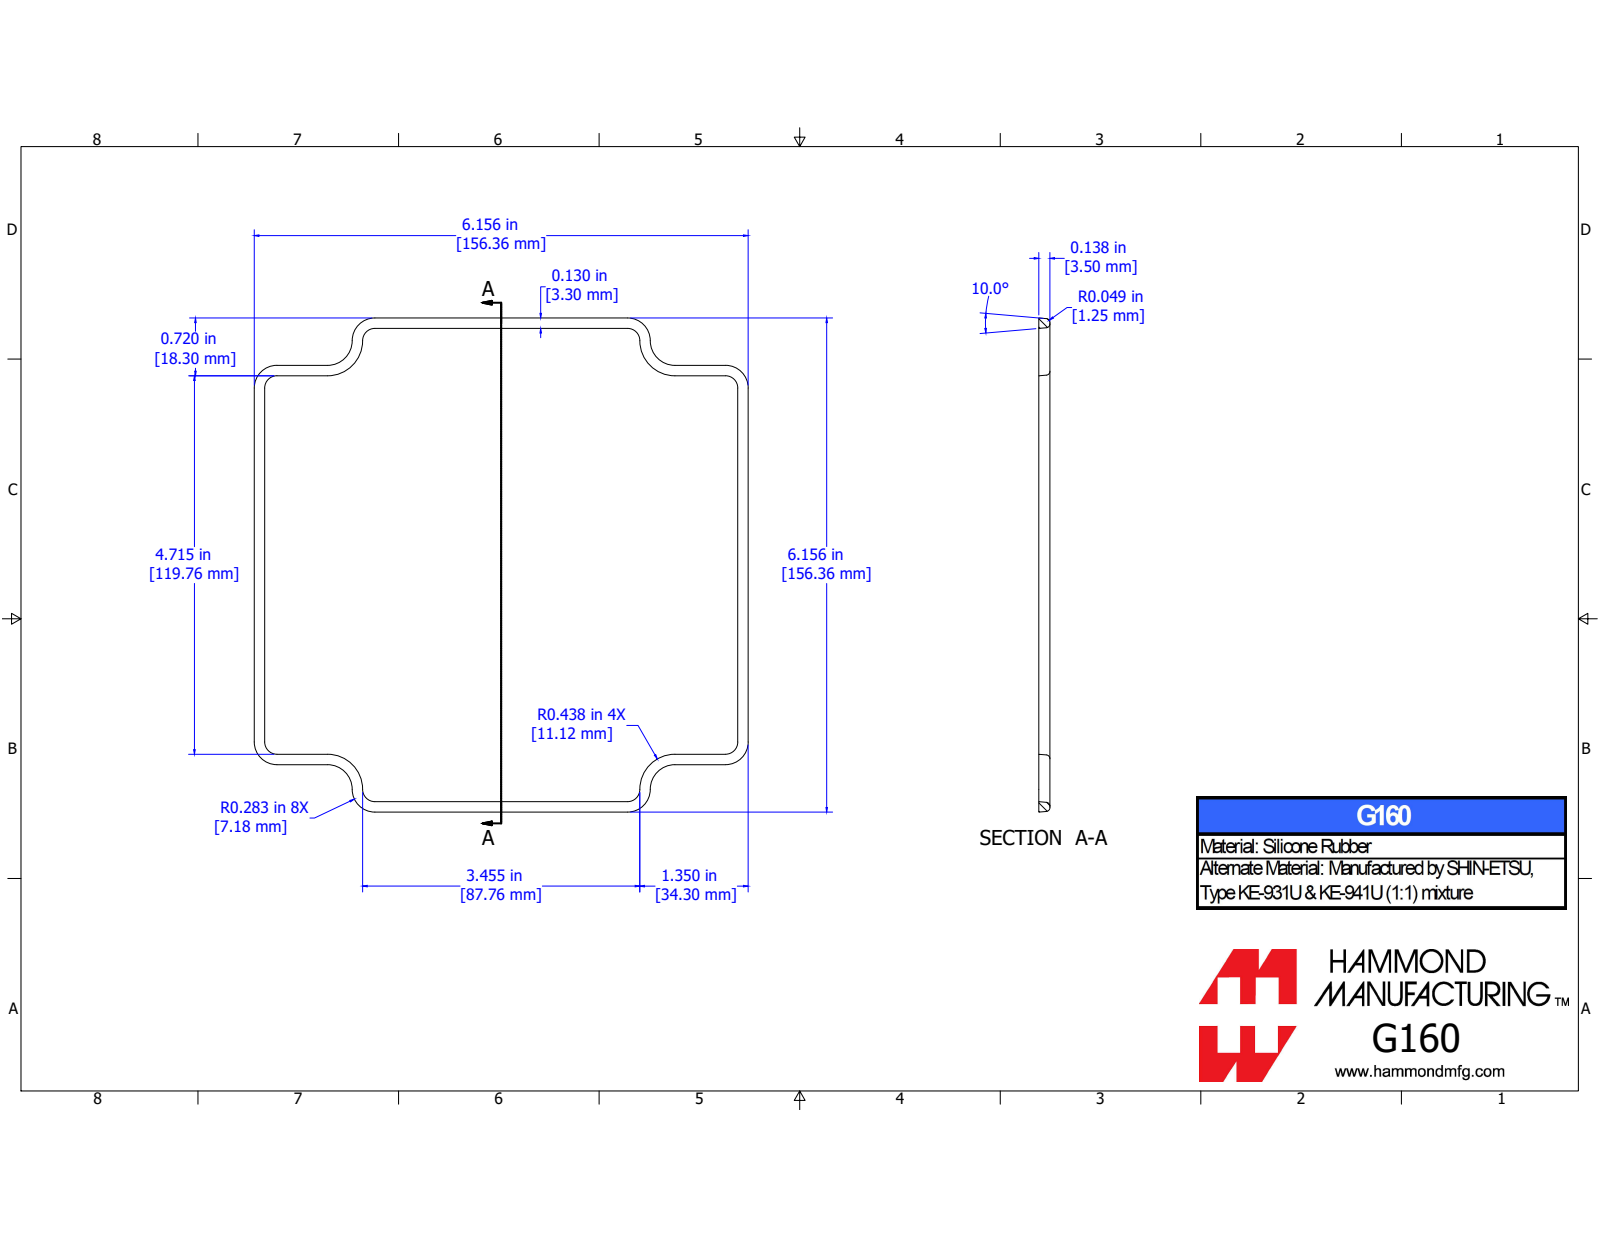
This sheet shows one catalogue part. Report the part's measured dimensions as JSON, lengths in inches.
{"part_name": "1590Z160G", "step_written_by": "SolidWorks 2019 (CONFIG_CONTROL_DESIGN)", "units": "inches", "bodies": {"solids": 1, "faces": 82, "planar": 18, "cylindrical": 16, "other": 48}, "overall_size": [6.146, 6.142, 0.138], "volume_in3": 0.319, "surface_area_in2": 10.4, "partial_cylinders_radius": [[0.039, 12]], "face_to_face_distances": [6.033, 6.037, 0.138, 0.622, 5.415, 4.793]}
